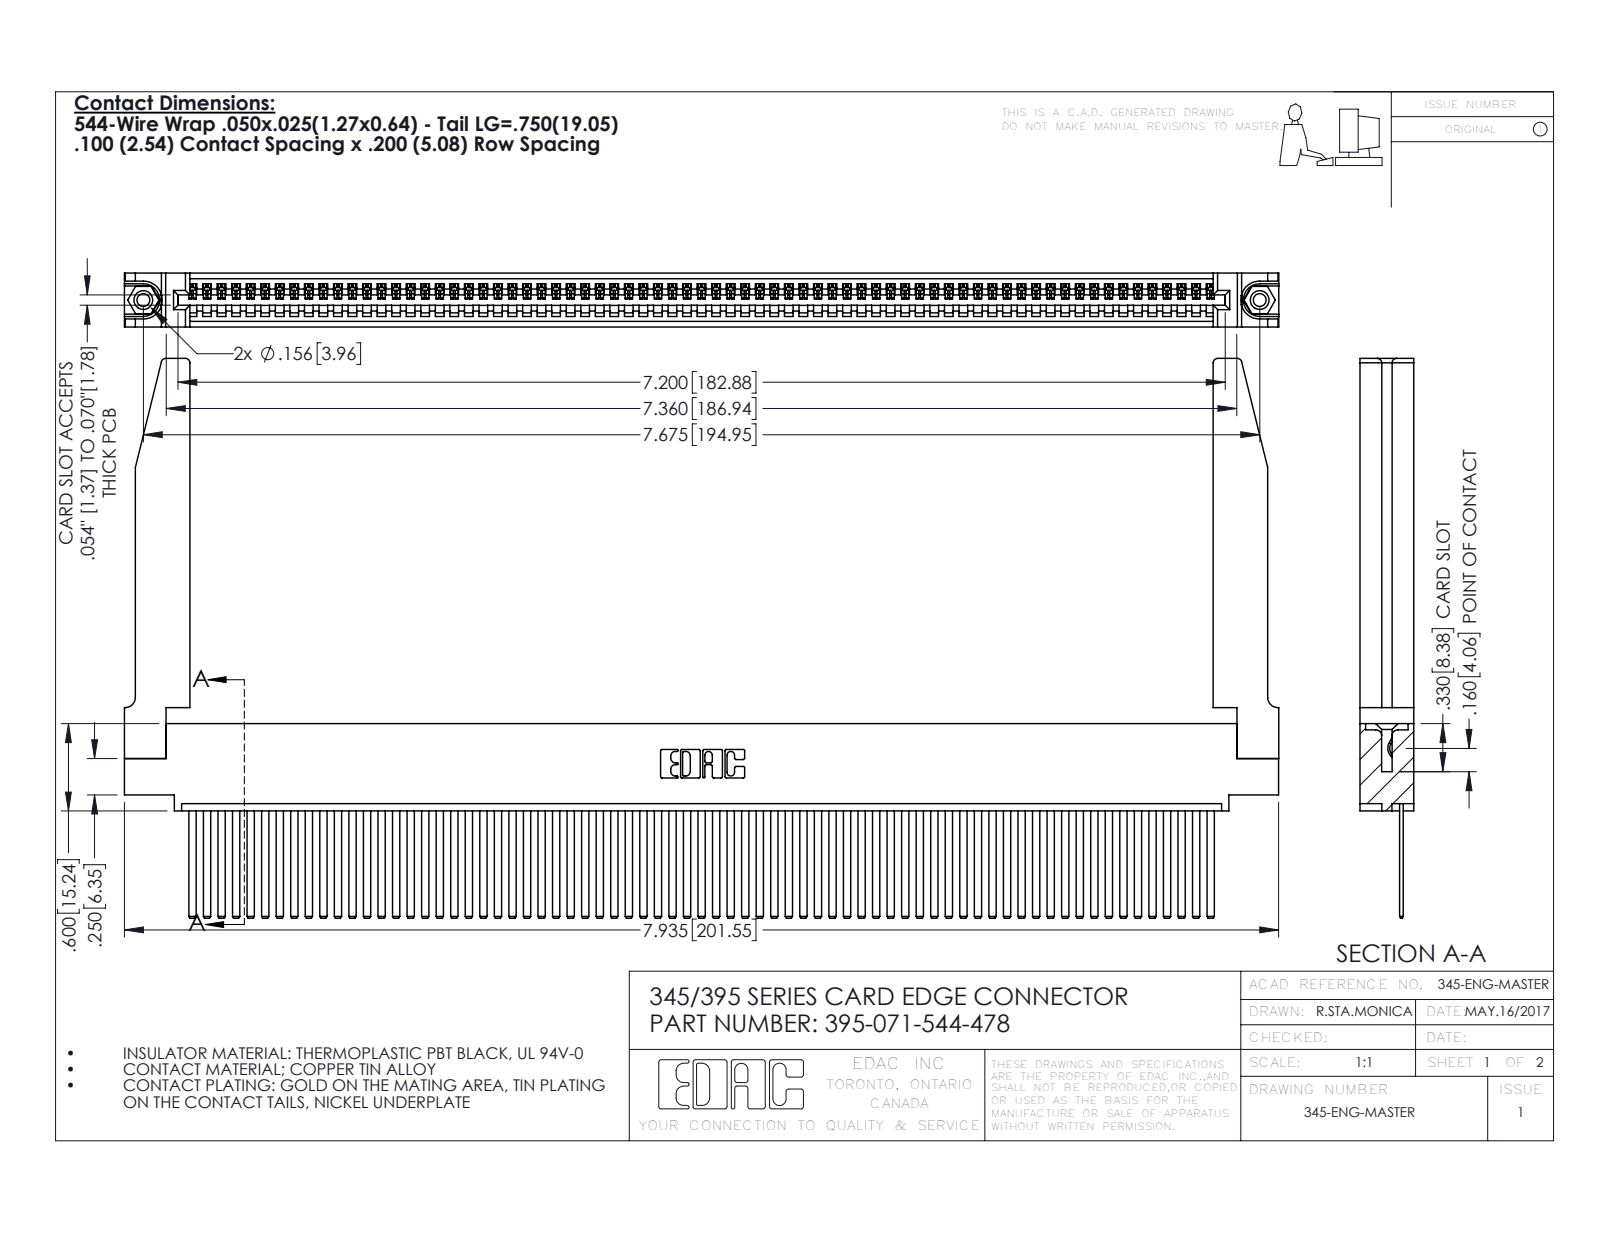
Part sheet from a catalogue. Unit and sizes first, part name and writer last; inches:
Units: inches
Overall size (bounding box): 7.936 × 3.847 × 0.37
Round holes (diameter × count): ⌀0.089 ×2, ⌀0.125 ×2, ⌀0.156 ×2, ⌀0.064 ×1
Round bosses / shafts (diameter × count): ⌀0.155 ×2
Partial cylindrical surfaces — rounded edges, fillets, slot ends (radius × count): R0.006 ×142, R0.01 ×22, R0.03 ×8, R0.007 ×6, R0.031 ×6, R0.026 ×3, R0.031 ×2, R0.04 ×2
Main face-to-face distances: 0.072, 0.298, 0.37, 0.098, 0.272, 0.025, 0.2, 0.225, 0.149, 0.148
Hole centre spacings: 0.27, 7.439, 7.675
Volume: 1.703 in³ · Surface area: 56.64 in²
Bodies: 76 solids, 4056 faces (2782 planar, 1222 cylindrical, 52 other)
Part name (STEP PRODUCT): 345-292-001_345-293-144; 345 Part_0.110 Offset - 0.156 Dia-TH; 395-071-544-478; 345-220-078_345-220-078 (+1 more)
STEP written by: SolidWorks 2016 (CONFIG_CONTROL_DESIGN)
